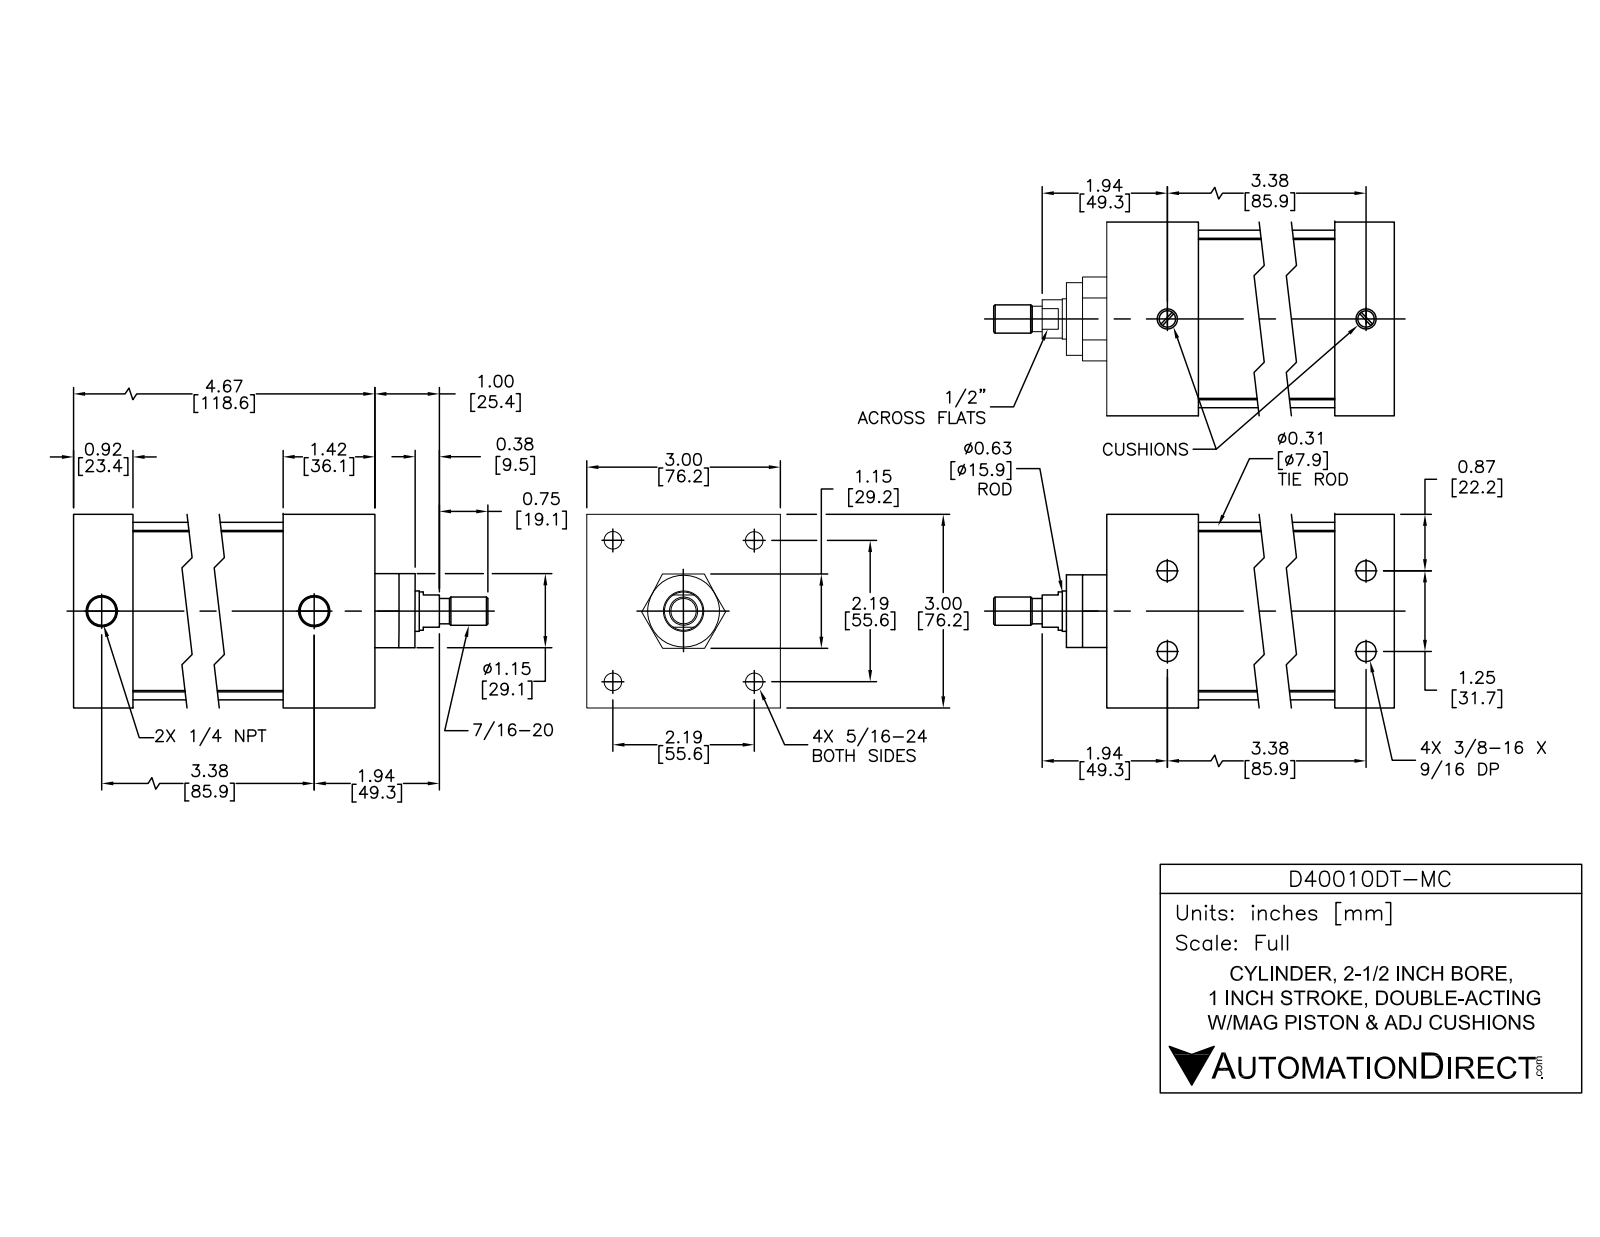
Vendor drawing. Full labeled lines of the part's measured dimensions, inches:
Part name (STEP PRODUCT): D40010DT-MC; D40010DT-M PISTON; D40010DT-M BODY
STEP written by: SolidWorks 2015 (AUTOMOTIVE_DESIGN)
Units: inches
Bodies: 12 solids, 298 faces (94 planar, 114 cylindrical, 90 other)
Overall size (bounding box): 6.496 × 3 × 3
Volume: 30.8 in³ · Surface area: 174.7 in²
Round holes (diameter × count): ⌀0.267 ×4, ⌀0.307 ×4, ⌀0.359 ×4, ⌀0.5 ×4, ⌀0.297 ×2, ⌀0.477 ×2, ⌀0.625 ×1, ⌀0.628 ×1, ⌀2.5 ×1
Round bosses / shafts (diameter × count): ⌀0.484 ×4, ⌀0.313 ×4, ⌀0.282 ×4, ⌀2.75 ×1, ⌀2.497 ×1, ⌀1.12 ×1, ⌀0.622 ×1, ⌀0.59 ×1
Partial cylindrical surfaces — rounded edges, fillets, slot ends (radius × count): R0.3 ×4
Main face-to-face distances: 3, 4.746, 3.726, 1.02, 1.42, 2.306, 3.326, 1, 3.826, 2.406
Hole centre spacings: 1.556, 2.2, 3.428, 3.37, 0.625, 0.625, 1.25, 3.111
